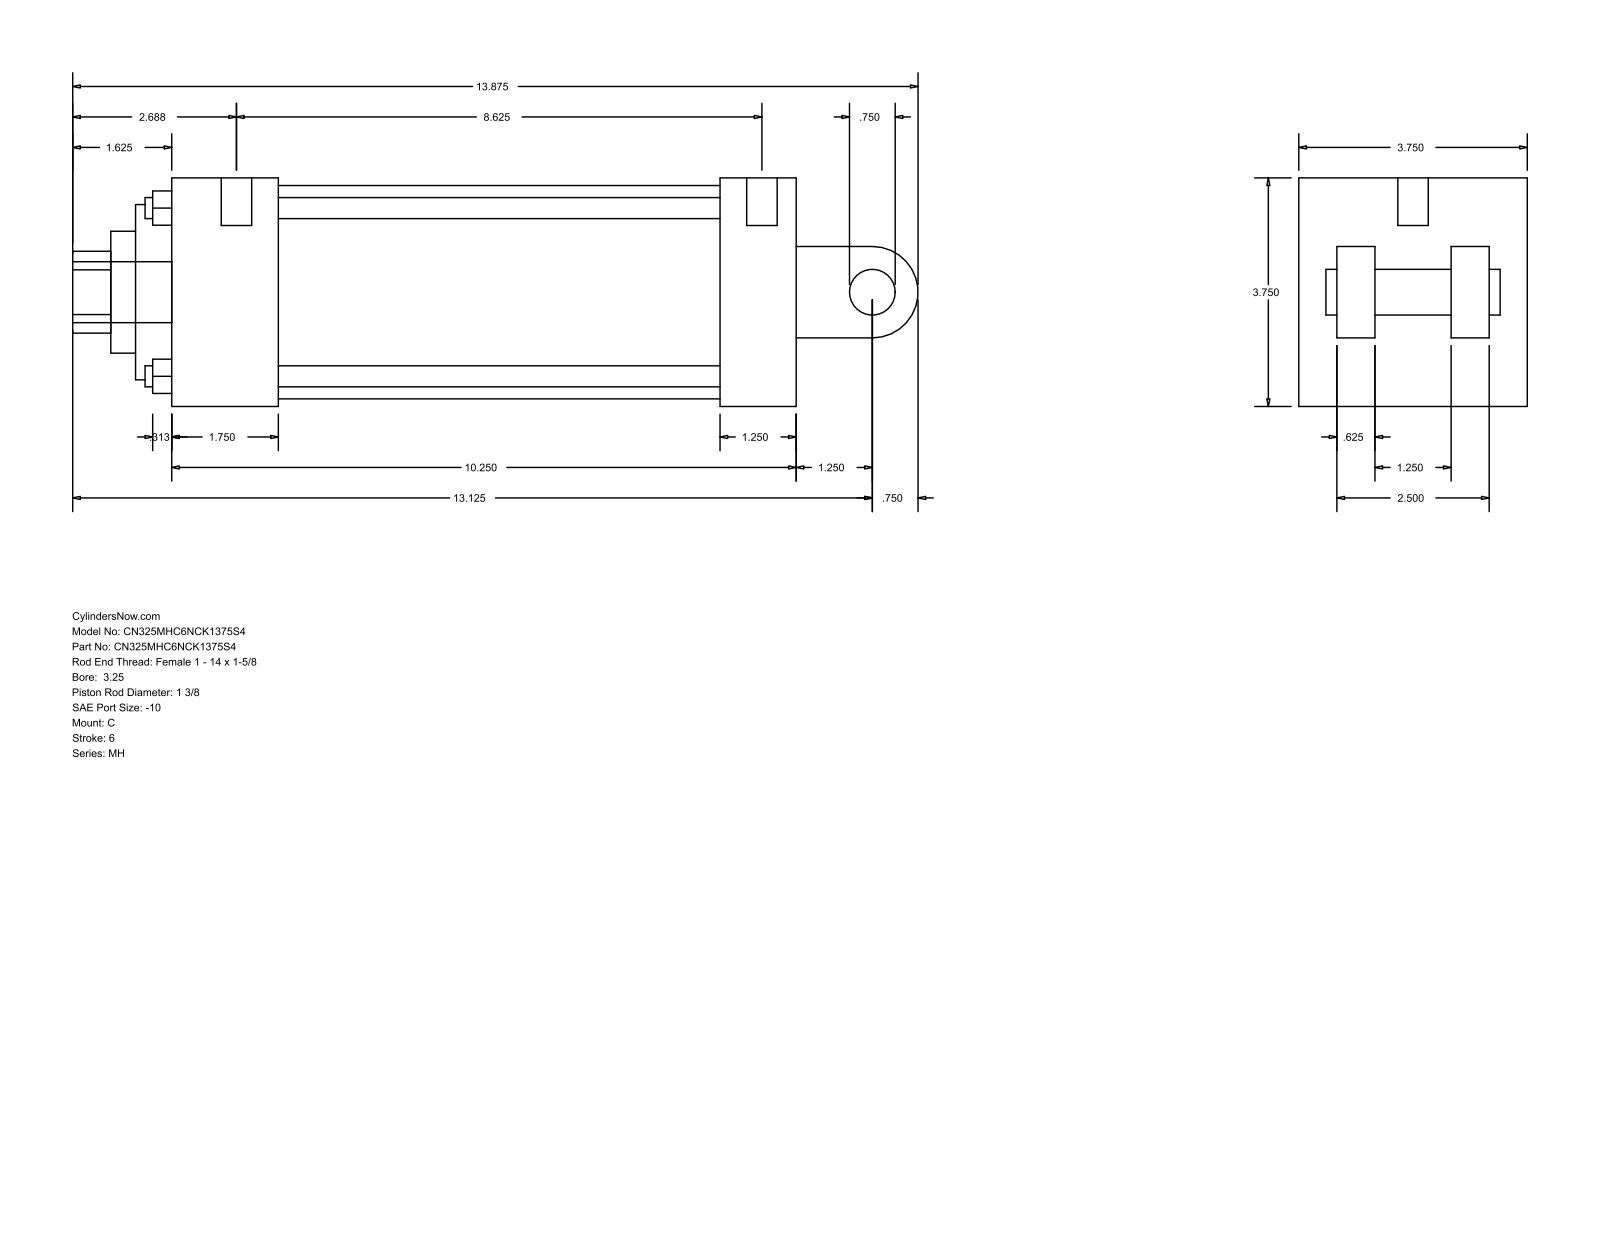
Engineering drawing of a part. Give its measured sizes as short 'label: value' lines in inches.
name: MH_C__0325_1.375
written by: GSSL Pune (CONFIG_CONTROL_DESIGN)
unit: in
bodies: 0 solids, 101 faces (71 planar, 30 cylindrical, 0 other)
size: 13.875 × 3.75 × 3.75
holes: 4× ⌀0.345, 2× ⌀0.219, 1× ⌀0.5, 1× ⌀1.375, 1× ⌀2, 1× ⌀2.875, 1× ⌀3.5
bosses: 2× ⌀0.219, 1× ⌀1, 1× ⌀0.75, 1× ⌀0.5
rounds: 1× R0.672, 1× R0.75
face distances: 3.75, 0.625, 1.25, 10.25, 2.5, 3.125, 1.875, 1.75, 9, 7.25
hole spacings: 1.952, 2.76, 3.903, 0.187
